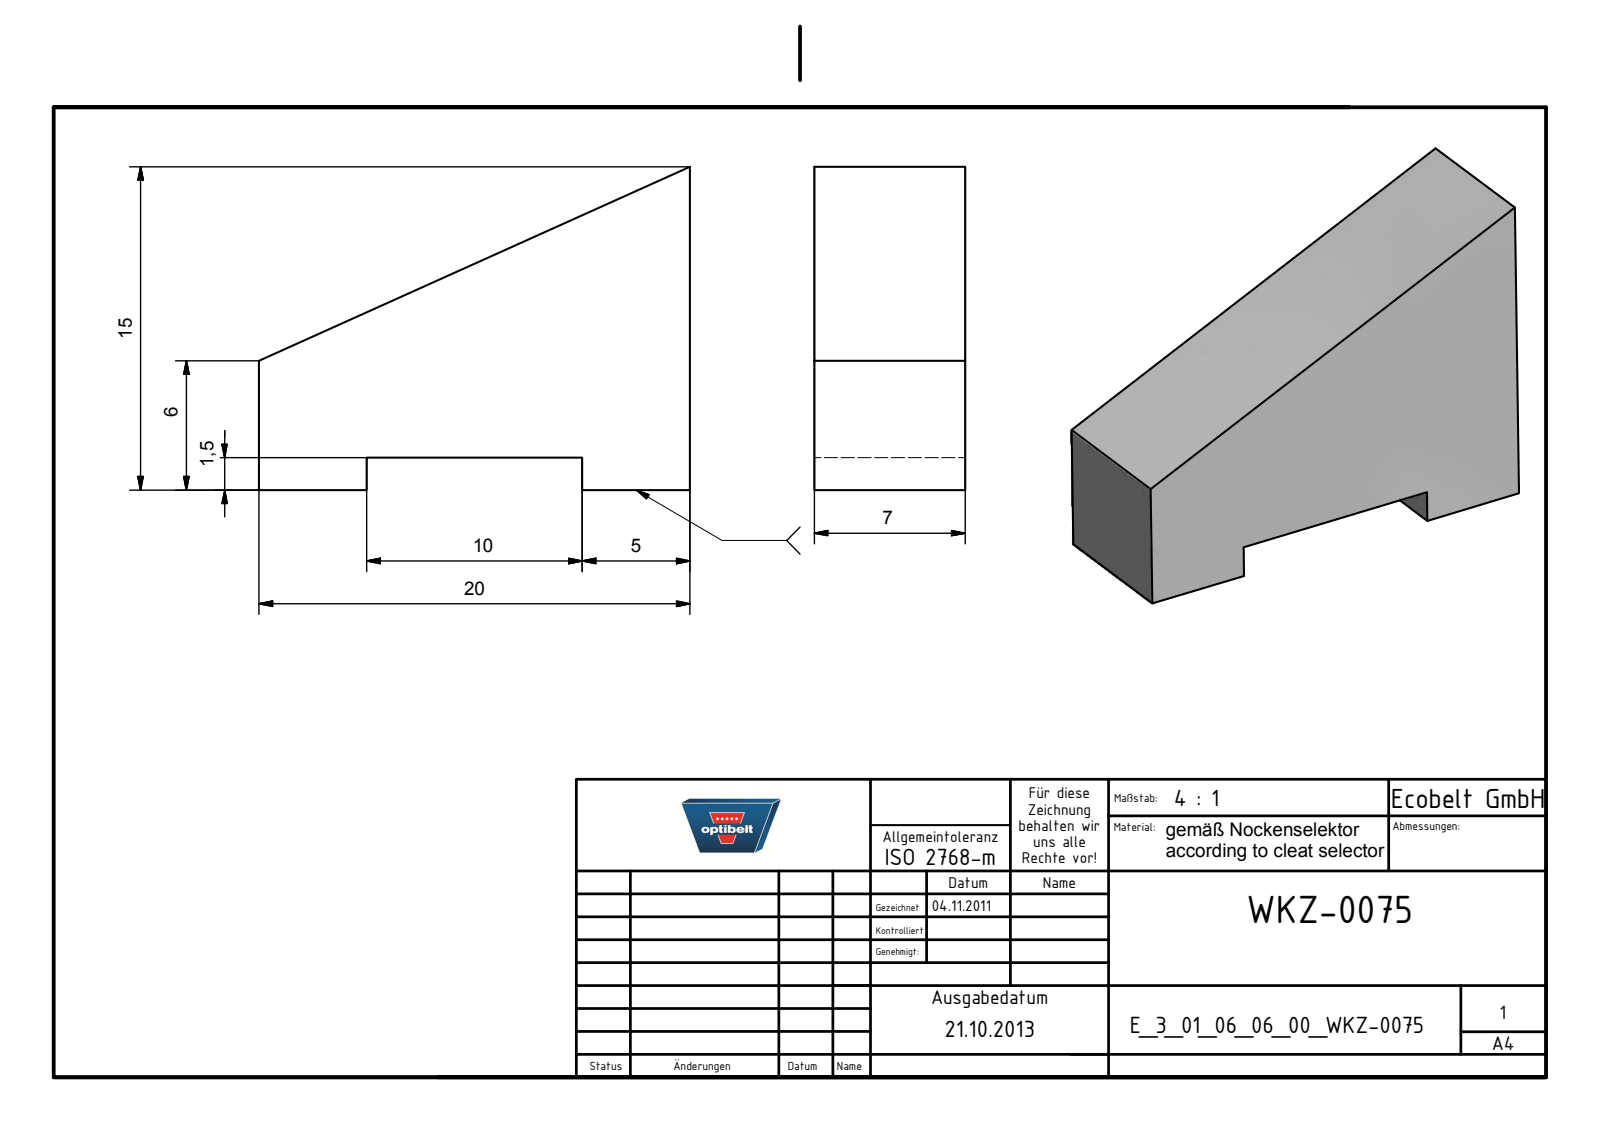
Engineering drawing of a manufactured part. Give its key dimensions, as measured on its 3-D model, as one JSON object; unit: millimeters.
{"part_name": "E_3_01_06_06_00_WKZ-0075", "step_written_by": "Autodesk Inventor 2025 (AUTOMOTIVE_DESIGN)", "units": "millimeters", "bodies": {"solids": 1, "faces": 10, "planar": 10, "cylindrical": 0, "other": 0}, "overall_size": [20, 15, 7], "volume_mm3": 1365, "surface_area_mm2": 852, "face_to_face_distances": [7, 1.5, 20, 5, 15, 10]}
